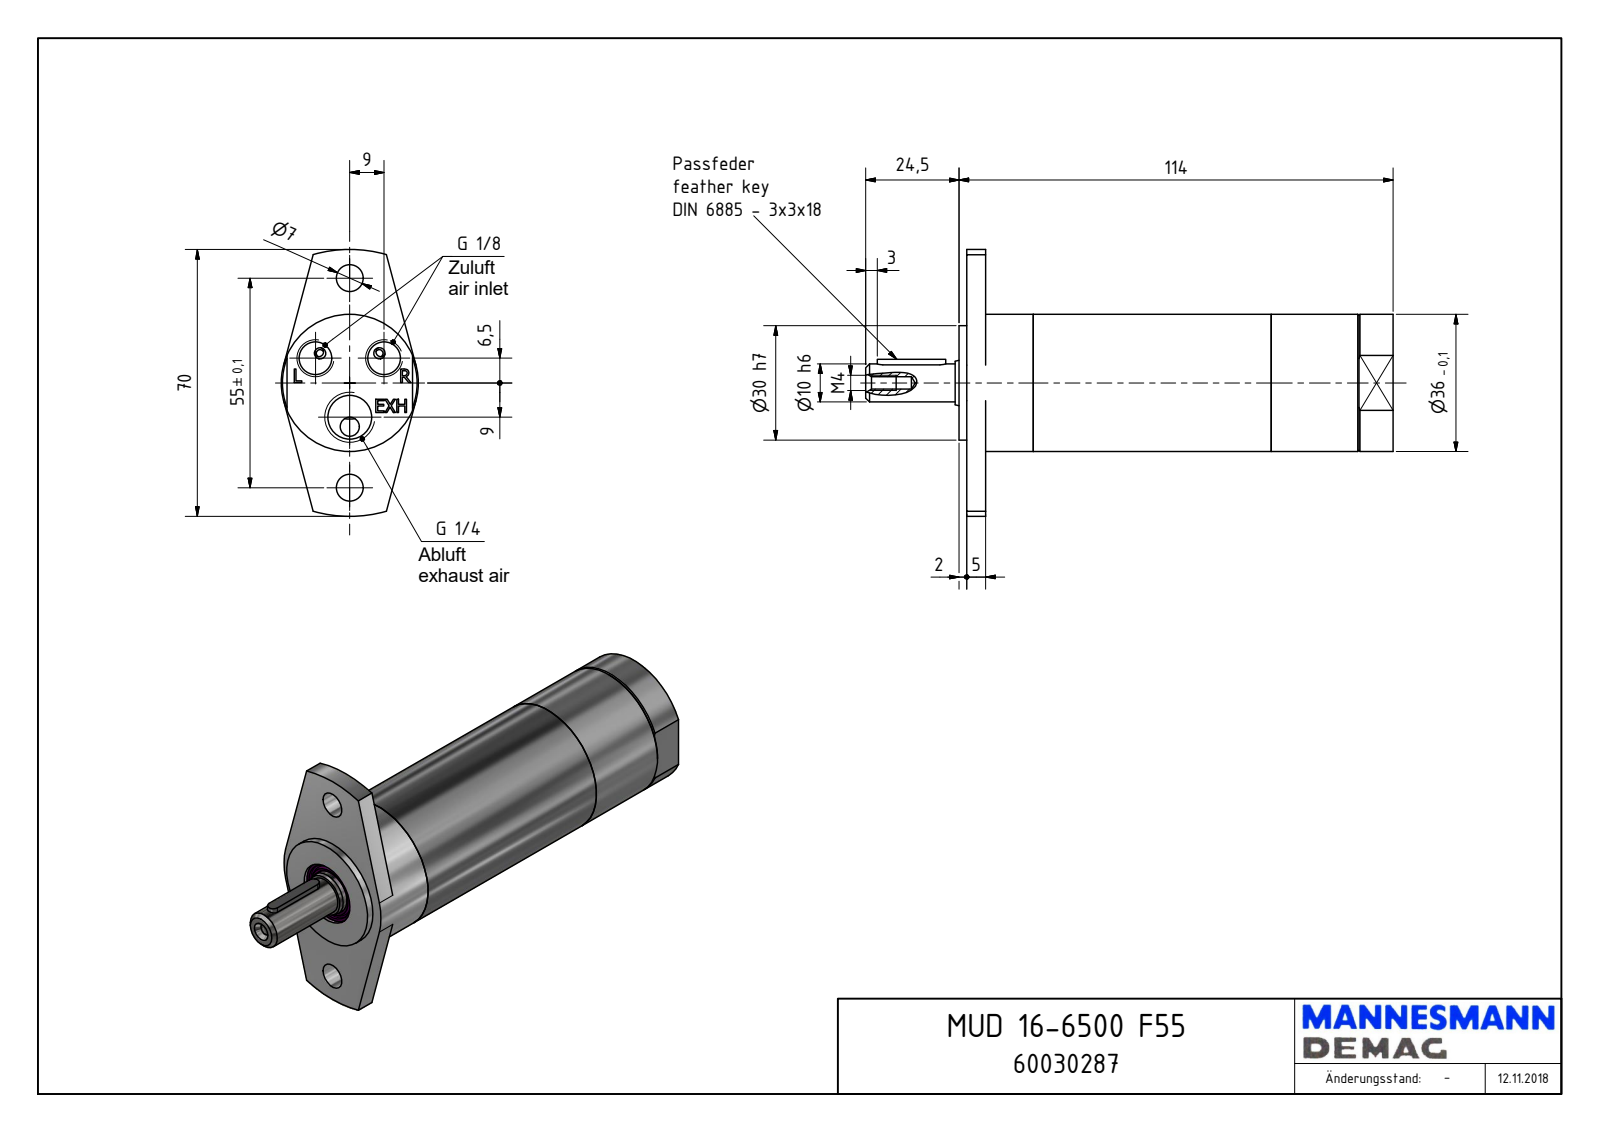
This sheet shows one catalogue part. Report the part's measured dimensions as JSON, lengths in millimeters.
{"part_name": "MUD 16-6500 F55_60030287", "step_written_by": "Autodesk Inventor 2018 (AUTOMOTIVE_DESIGN)", "units": "millimeters", "bodies": {"solids": 1, "faces": 123, "planar": 82, "cylindrical": 20, "other": 21}, "overall_size": [138.5, 70, 36], "volume_mm3": 118798, "surface_area_mm2": 19224, "round_holes": [[7, 2], [8.57, 2], [3.24, 1], [11.45, 1], [15.5, 1], [17, 1]], "round_bosses_or_shafts": [[36, 1], [30, 1], [11.95, 1], [10, 1]], "partial_cylinders_radius": [[1.5, 2], [35, 1]], "face_to_face_distances": [5, 112, 107, 2, 7, 114, 103.75, 101.75, 96.75, 10.25], "hole_center_spacings": [11.1, 17.92, 22.85, 27.5, 35.17, 9, 18, 18.5]}
